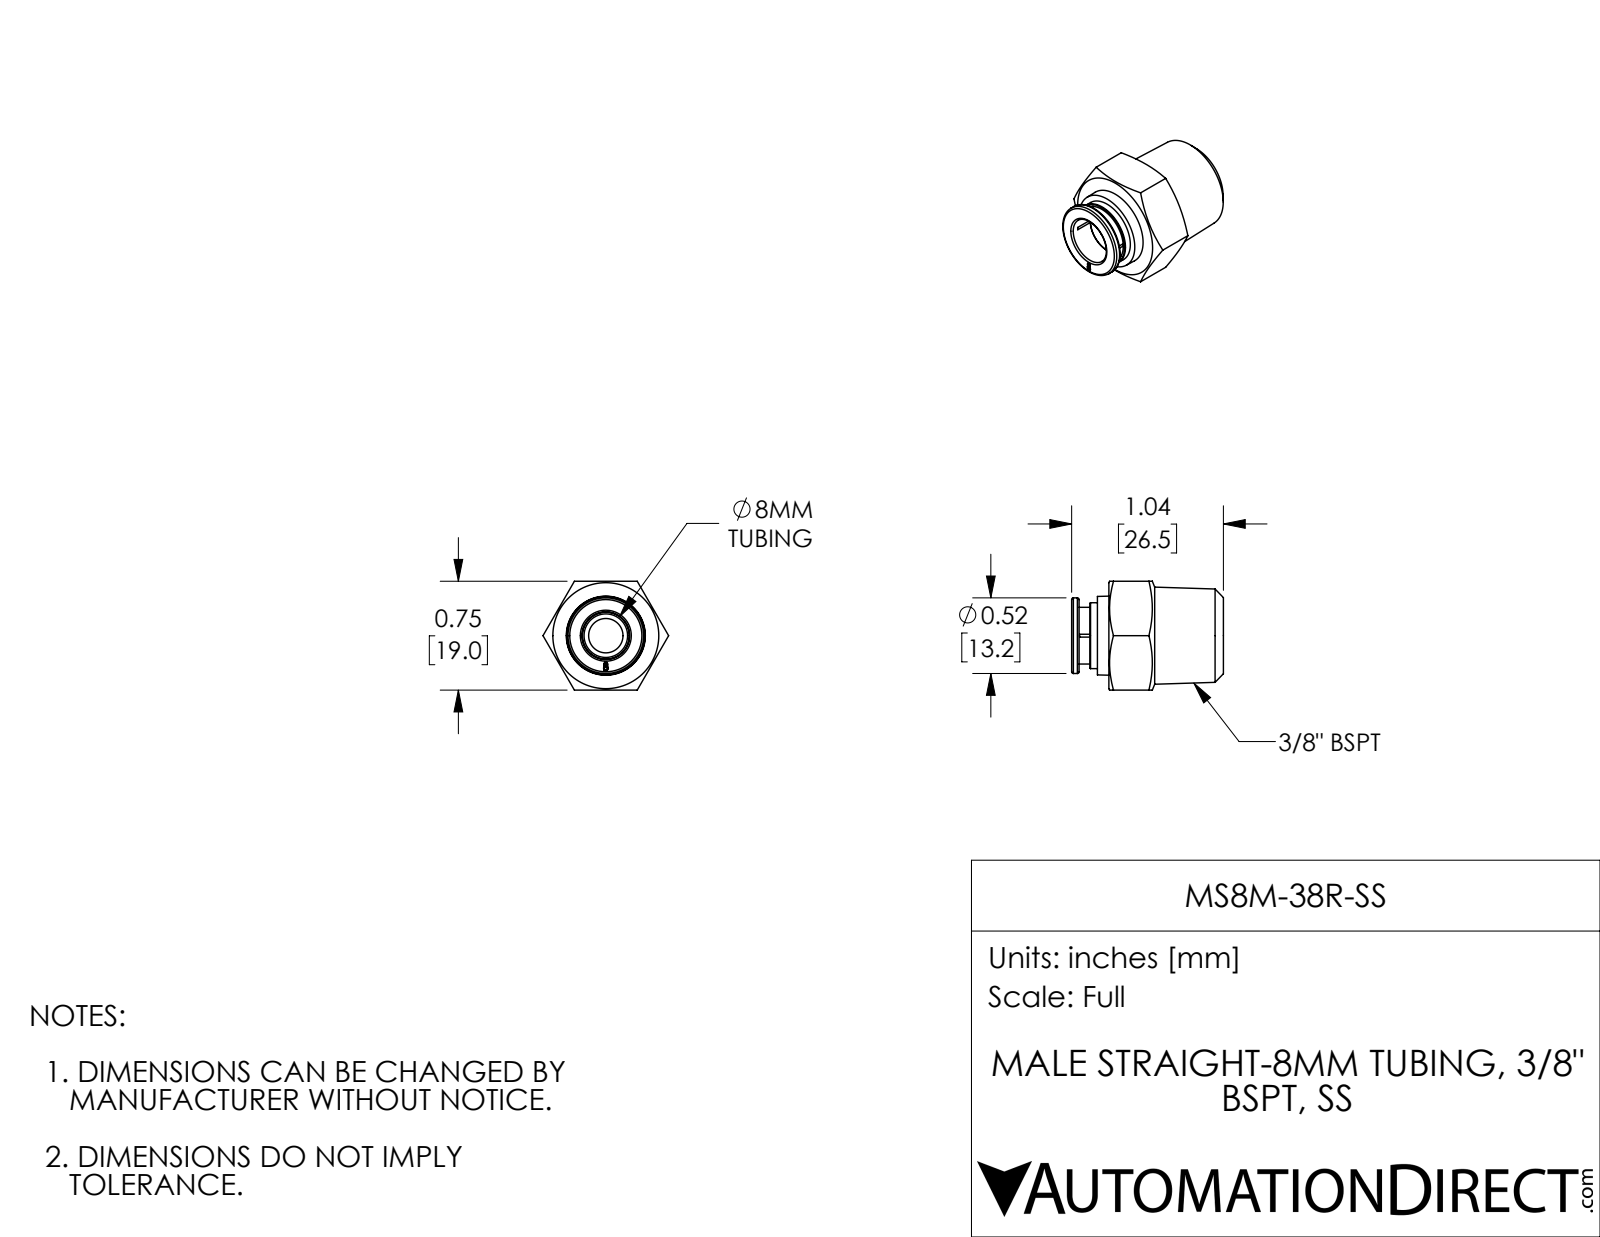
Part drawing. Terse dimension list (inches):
name: MS8M-38R-SS
written by: SolidWorks 2017 (AUTOMOTIVE_DESIGN)
unit: in
bodies: 1 solid, 75 faces (23 planar, 14 cylindrical, 38 other)
size: 1.043 × 0.864 × 0.748
volume: 0.277 in³; area: 4.097 in²
holes: 1× ⌀0.236, 1× ⌀0.323, 1× ⌀0.327, 1× ⌀0.394
bosses: 1× ⌀0.52, 1× ⌀0.453, 1× ⌀0.39
face distances: 0.748, 0.787, 1.043, 0.256, 0.051, 0.126, 0.992, 0.205, 0.866, 0.079
